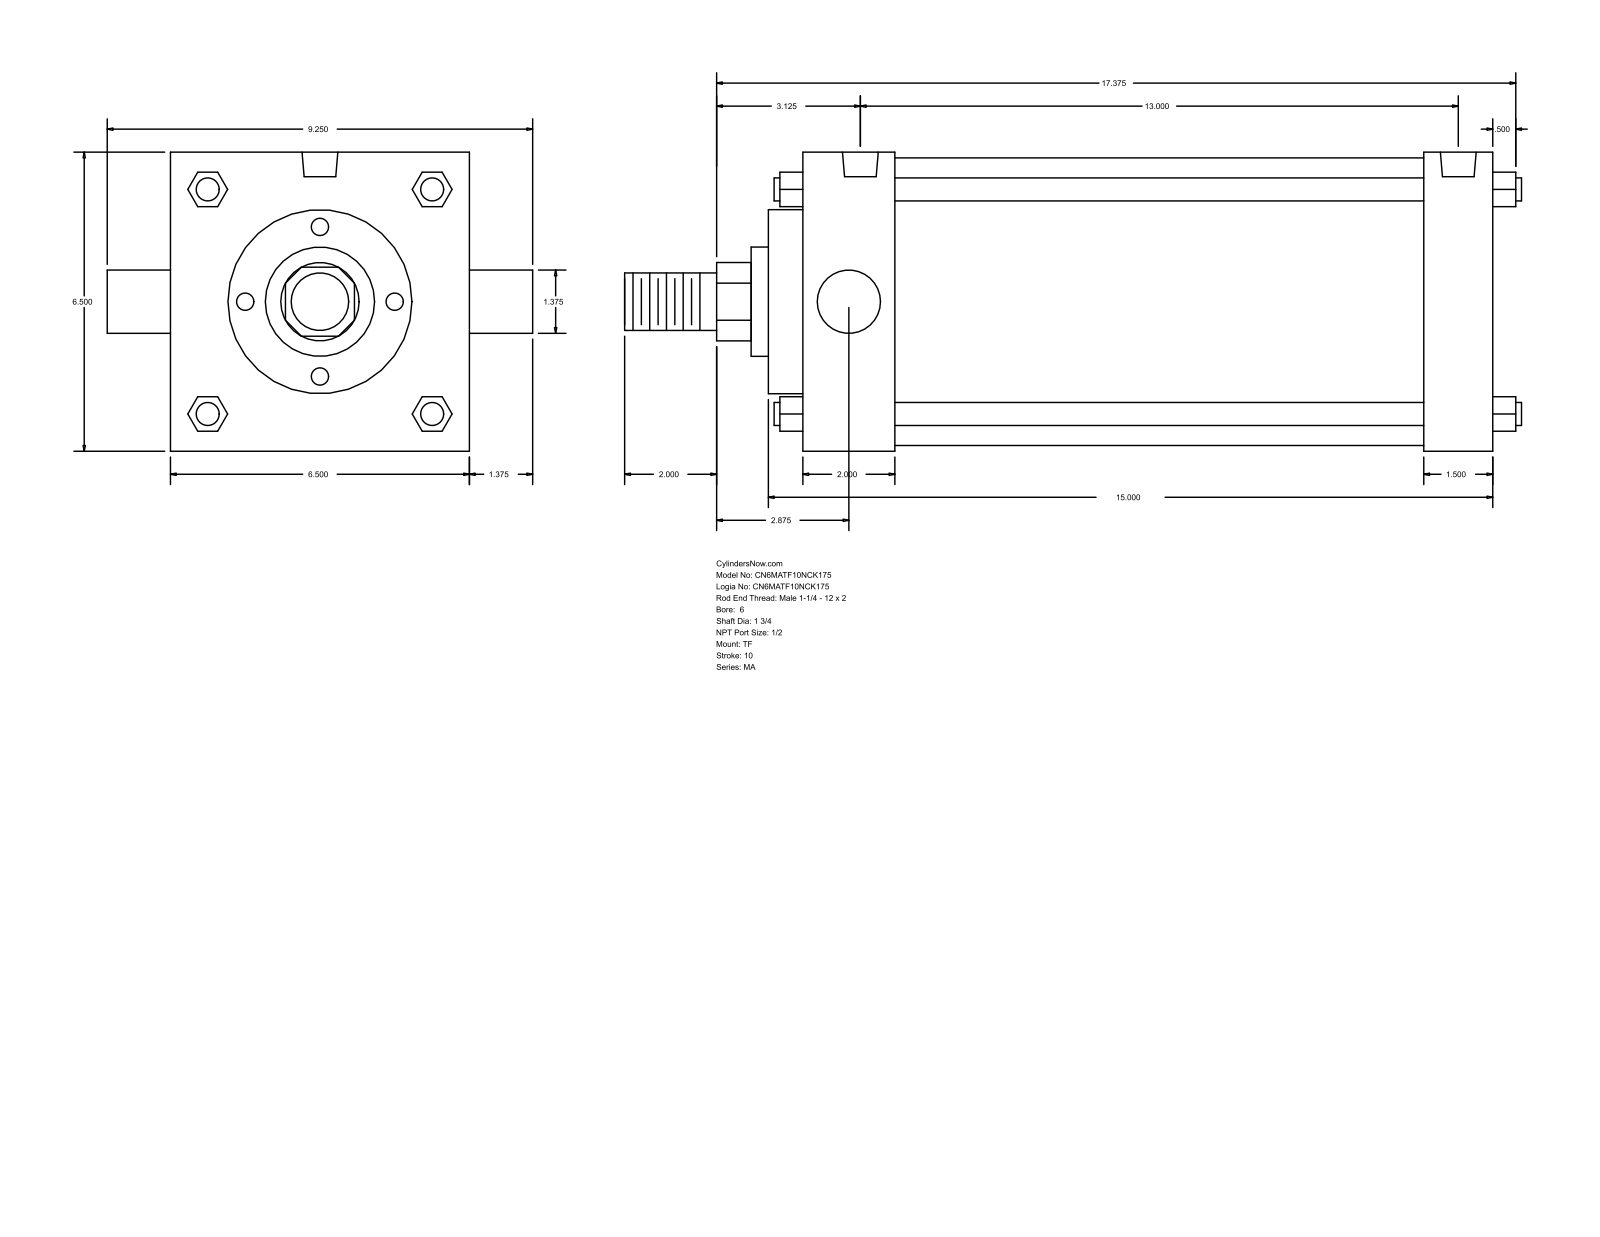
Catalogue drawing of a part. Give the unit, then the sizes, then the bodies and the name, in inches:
Units: inches
Overall size (bounding box): 19.5 × 9.25 × 6.5
Round holes (diameter × count): ⌀0.687 ×3, ⌀0.778 ×2
Round bosses / shafts (diameter × count): ⌀0.5 ×4, ⌀6.25 ×1, ⌀4 ×1, ⌀2.375 ×1, ⌀1.75 ×1, ⌀1.375 ×1, ⌀1.25 ×1
Partial cylindrical surfaces — rounded edges, fillets, slot ends (radius × count): R0.852 ×1
Main face-to-face distances: 6.5, 15, 0.75, 2, 13.5, 1.5, 13, 11.5, 2.75, 14.25
Hole centre spacings: 13
Bodies: 0 solids, 122 faces (93 planar, 29 cylindrical, 0 other)
Part name (STEP PRODUCT): MA_TF__0600_1.75
STEP written by: GSSL Pune (CONFIG_CONTROL_DESIGN)
